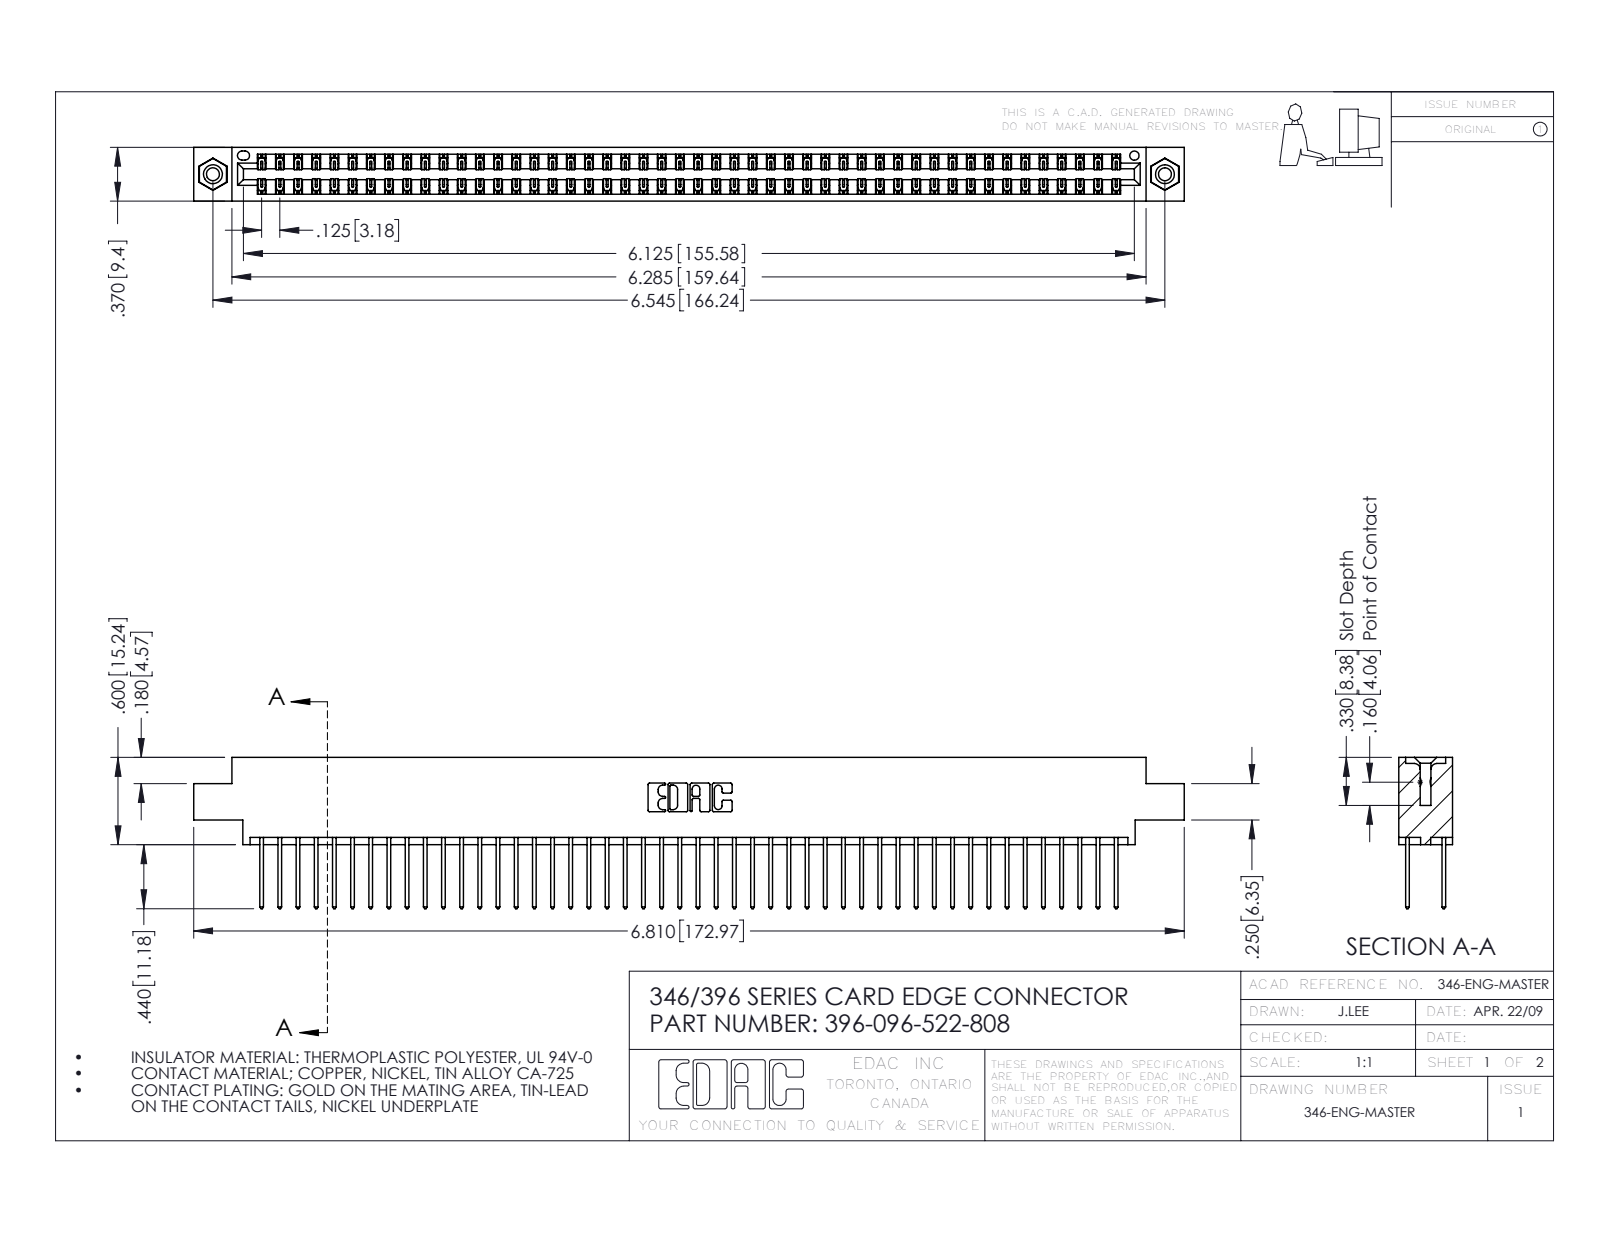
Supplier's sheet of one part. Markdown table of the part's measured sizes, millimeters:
| quantity | value |
| --- | --- |
| part name | 345-250-001_345-250-003-102; 345-292-001_345-293-122; 346 Part_0.170 Offset - 0.156 Dia-TI; 396-096-522-808 |
| STEP written by | SolidWorks 2016 (CONFIG_CONTROL_DESIGN) |
| units | millimeters |
| bodies | 99 solids, 5178 faces (3472 planar, 1690 cylindrical, 16 other) |
| overall size | 173 × 26.4 × 9.4 |
| volume | 16 990 mm³ |
| surface area | 24 800 mm² |
| round holes (diameter × count) | 2.3 × 2, 3.2 × 2, 4 × 2, 1.6 × 1 |
| round bosses / shafts (diameter × count) | 3.9 × 2 |
| partial cylindrical surfaces (radius × count) | 0.2 × 144, 0.3 × 96, 0.3 × 22, 0.2 × 6, 0.8 × 6, 0.7 × 3, 0.4 × 2, 0.6 × 2 |
| main face-to-face distances | 1.2, 8.2, 6.4, 9.4, 1.8, 7.6, 0.6, 7, 5.6, 3.8 |
| hole center spacings | 6.2, 160.9, 166.2 |
